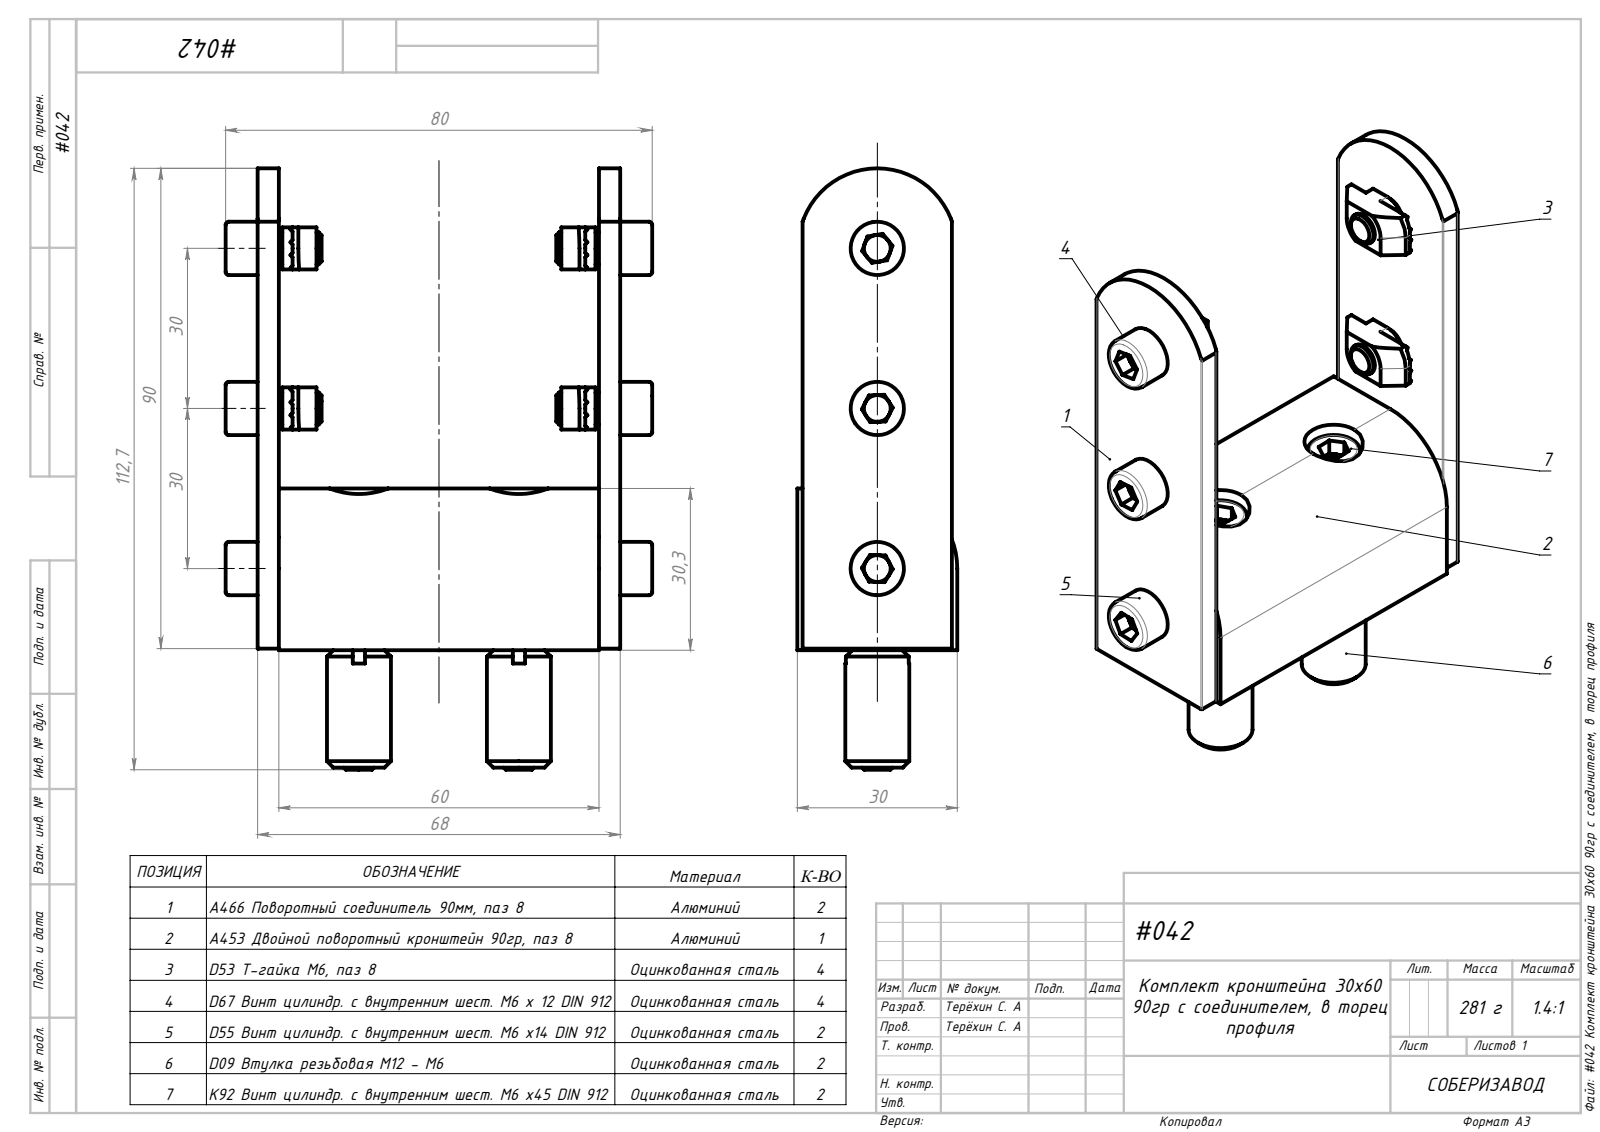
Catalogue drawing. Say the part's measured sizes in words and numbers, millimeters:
The part is named "#042 Комплект кронштейна 30х60 90гр с соединителем, в торец профиля; D53 Т-гайка М6, паз 8_00; A466 Поворотный соединитель 90мм, паз 8; D55 Винт цилиндр. с внутренним шест. М6 х14 DIN 912 (+4 more)". Its 3-D file was written by "SolidWorks 2021 (AUTOMOTIVE_DESIGN)". It is 17 solids with 505 faces: 284 planar, 101 cylindrical and 120 other. Overall it measures 112.7 by 80 by 30 millimeters. Its volume is 79 884 cubic millimeters and its surface area 32 977 square millimeters. Round holes: 3 of diameter 6.4, 2 of diameter 5, 2 of diameter 5.5, 2 of diameter 6.15, 2 of diameter 11, 1 of diameter 5.15. Round bosses or shafts: 5 of diameter 10, 5 of diameter 6, 2 of diameter 12. Partial cylindrical surfaces (rounded edges, fillets, slot ends): 8 of radius 0.2, 8 of radius 4, 4 of radius 6.87, 1 of radius 14.8, 1 of radius 15. The main face-to-face distances are 4, 64, 60, 68, 30, 1, 29, 30.3, 28, 6. The hole center spacings are 30, 60.
